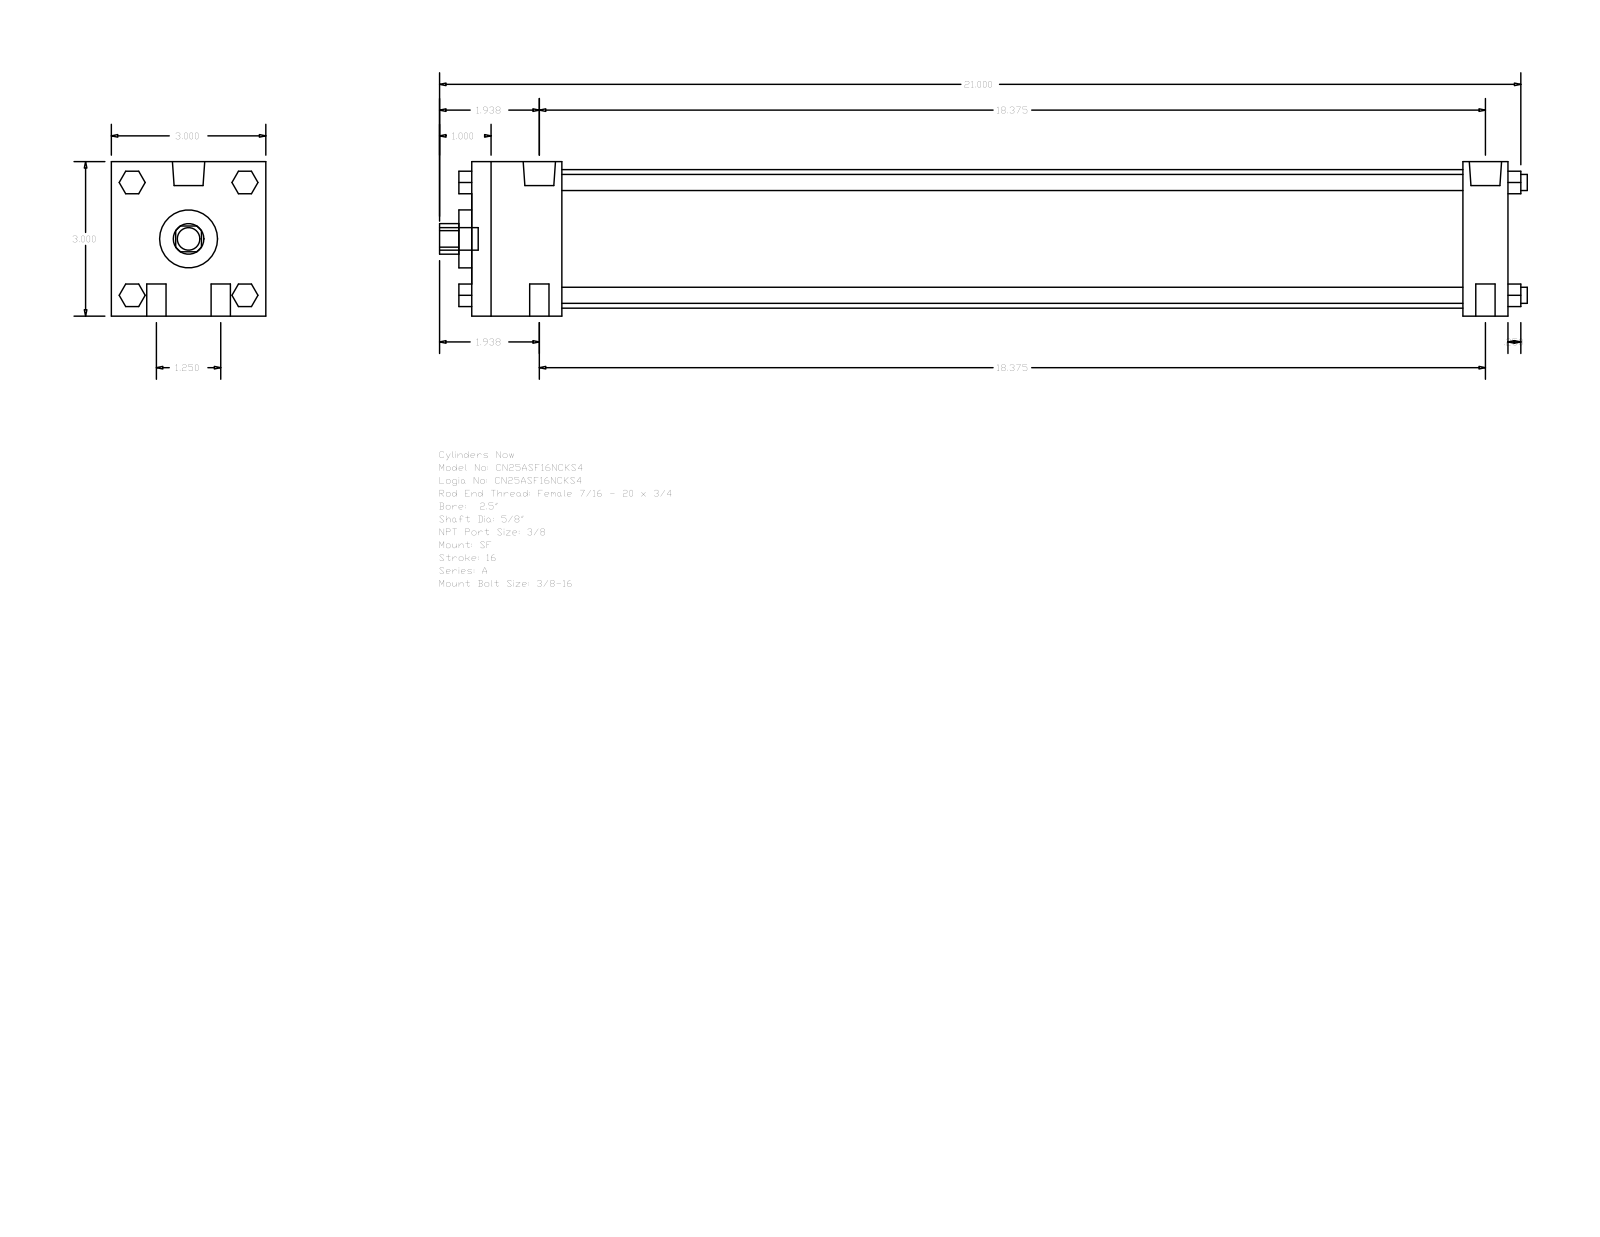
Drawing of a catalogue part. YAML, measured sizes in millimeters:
part_name: "A_SF__0250_0.625"
step_written_by: "GSSL Pune (CONFIG_CONTROL_DESIGN)"
units: millimeters
bodies: {solids: 0, faces: 124, planar: 94, cylindrical: 30, other: 0}
overall_size: [536.58, 76.2, 76.2]
round_holes:
  - {diameter: 15.88, count: 1}
  - {diameter: 28.57, count: 1}
  - {diameter: 68.33, count: 1}
round_bosses_or_shafts:
  - {diameter: 9.53, count: 4}
  - {diameter: 7.94, count: 4}
  - {diameter: 15.93, count: 2}
  - {diameter: 5.56, count: 2}
  - {diameter: 11.11, count: 1}
partial_cylinders:
  - {radius: 7.54, count: 1}
face_to_face_distances: [76.2, 511.17, 44.45, 488.94, 22.23, 444.49, 466.72, 6.35, 517.52, 50.8]
